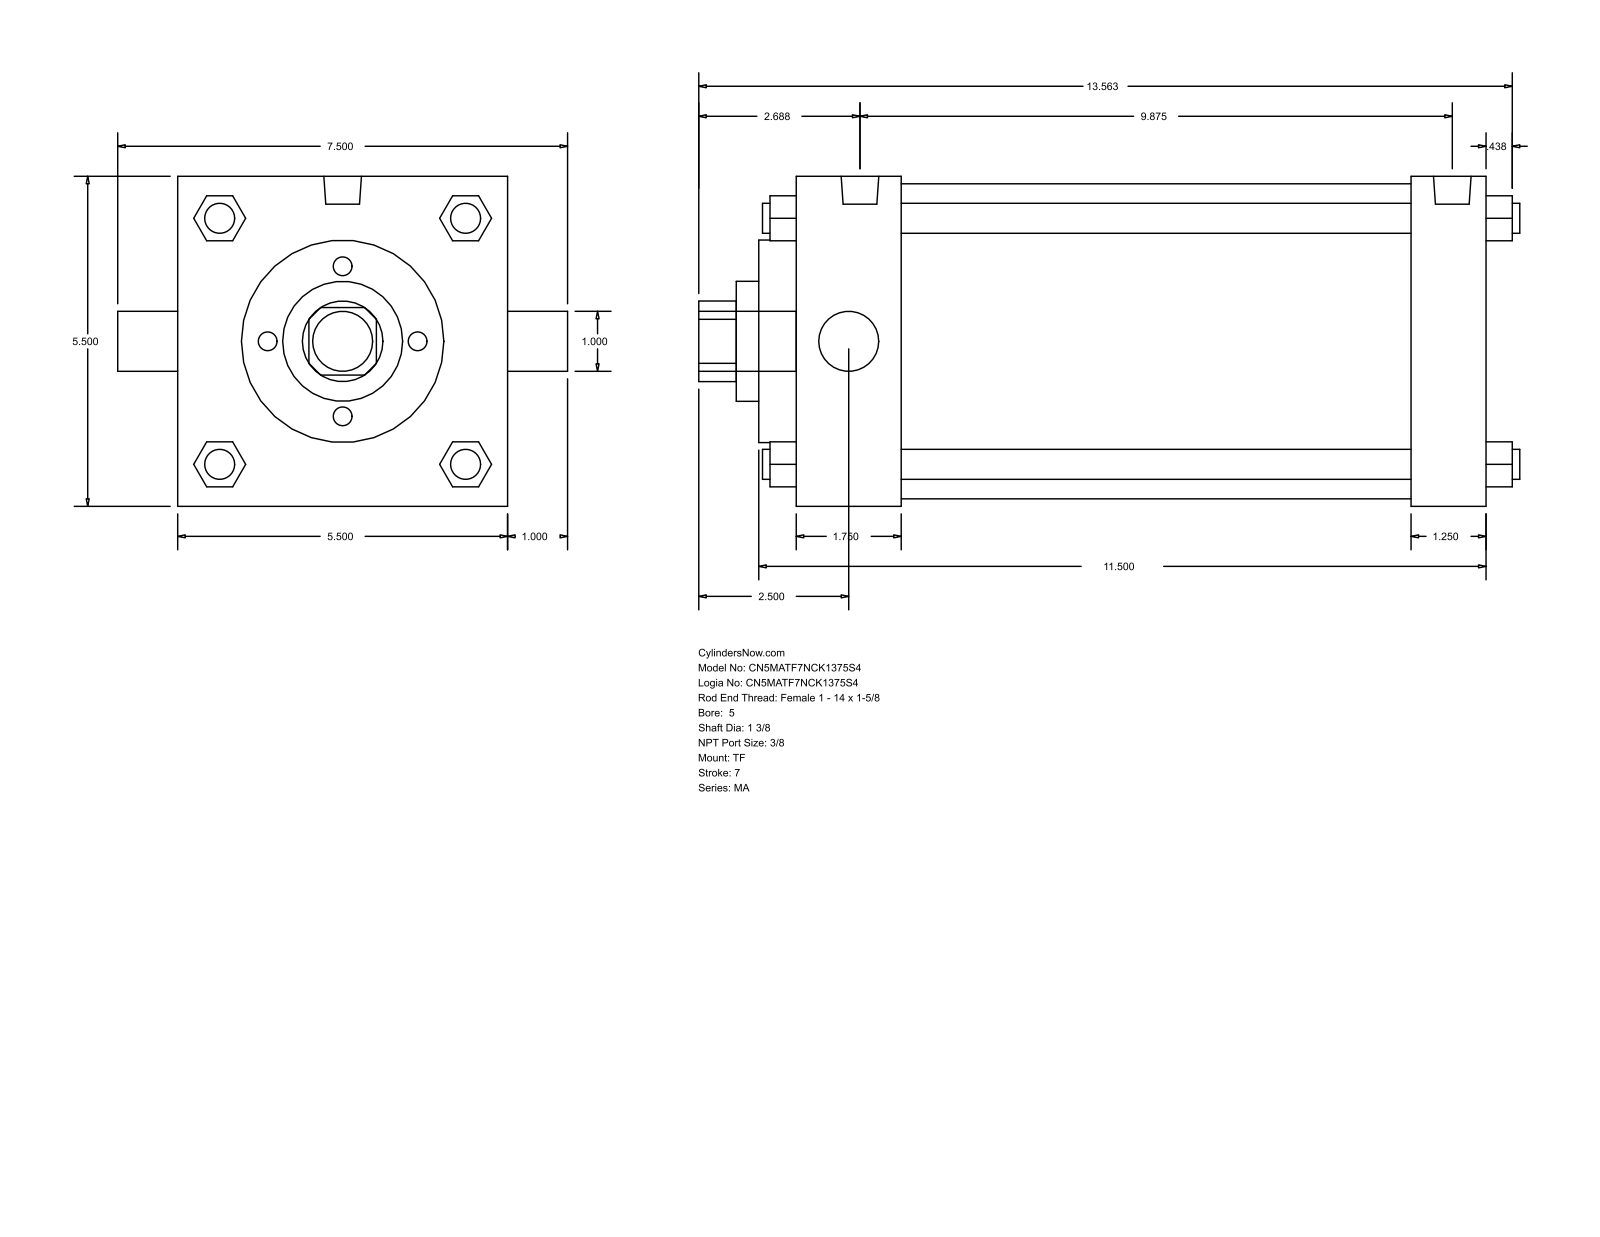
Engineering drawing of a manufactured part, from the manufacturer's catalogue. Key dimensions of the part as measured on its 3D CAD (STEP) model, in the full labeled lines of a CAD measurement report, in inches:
Part name (STEP PRODUCT): MA_TF__0500_1.375
STEP written by: GSSL Pune (CONFIG_CONTROL_DESIGN)
Units: inches
Bodies: 0 solids, 122 faces (93 planar, 29 cylindrical, 0 other)
Overall size (bounding box): 13.687 × 7.5 × 5.5
Round holes (diameter × count): ⌀1 ×1, ⌀1.375 ×1, ⌀2 ×1, ⌀3.375 ×1, ⌀5.25 ×1
Round bosses / shafts (diameter × count): ⌀0.5 ×4, ⌀0.437 ×3, ⌀0.627 ×2, ⌀1 ×1
Partial cylindrical surfaces — rounded edges, fillets, slot ends (radius × count): R0.672 ×1
Main face-to-face distances: 5.5, 11.5, 10.25, 1.25, 1.75, 8.5, 9.75, 0.625, 2.375, 10.875
